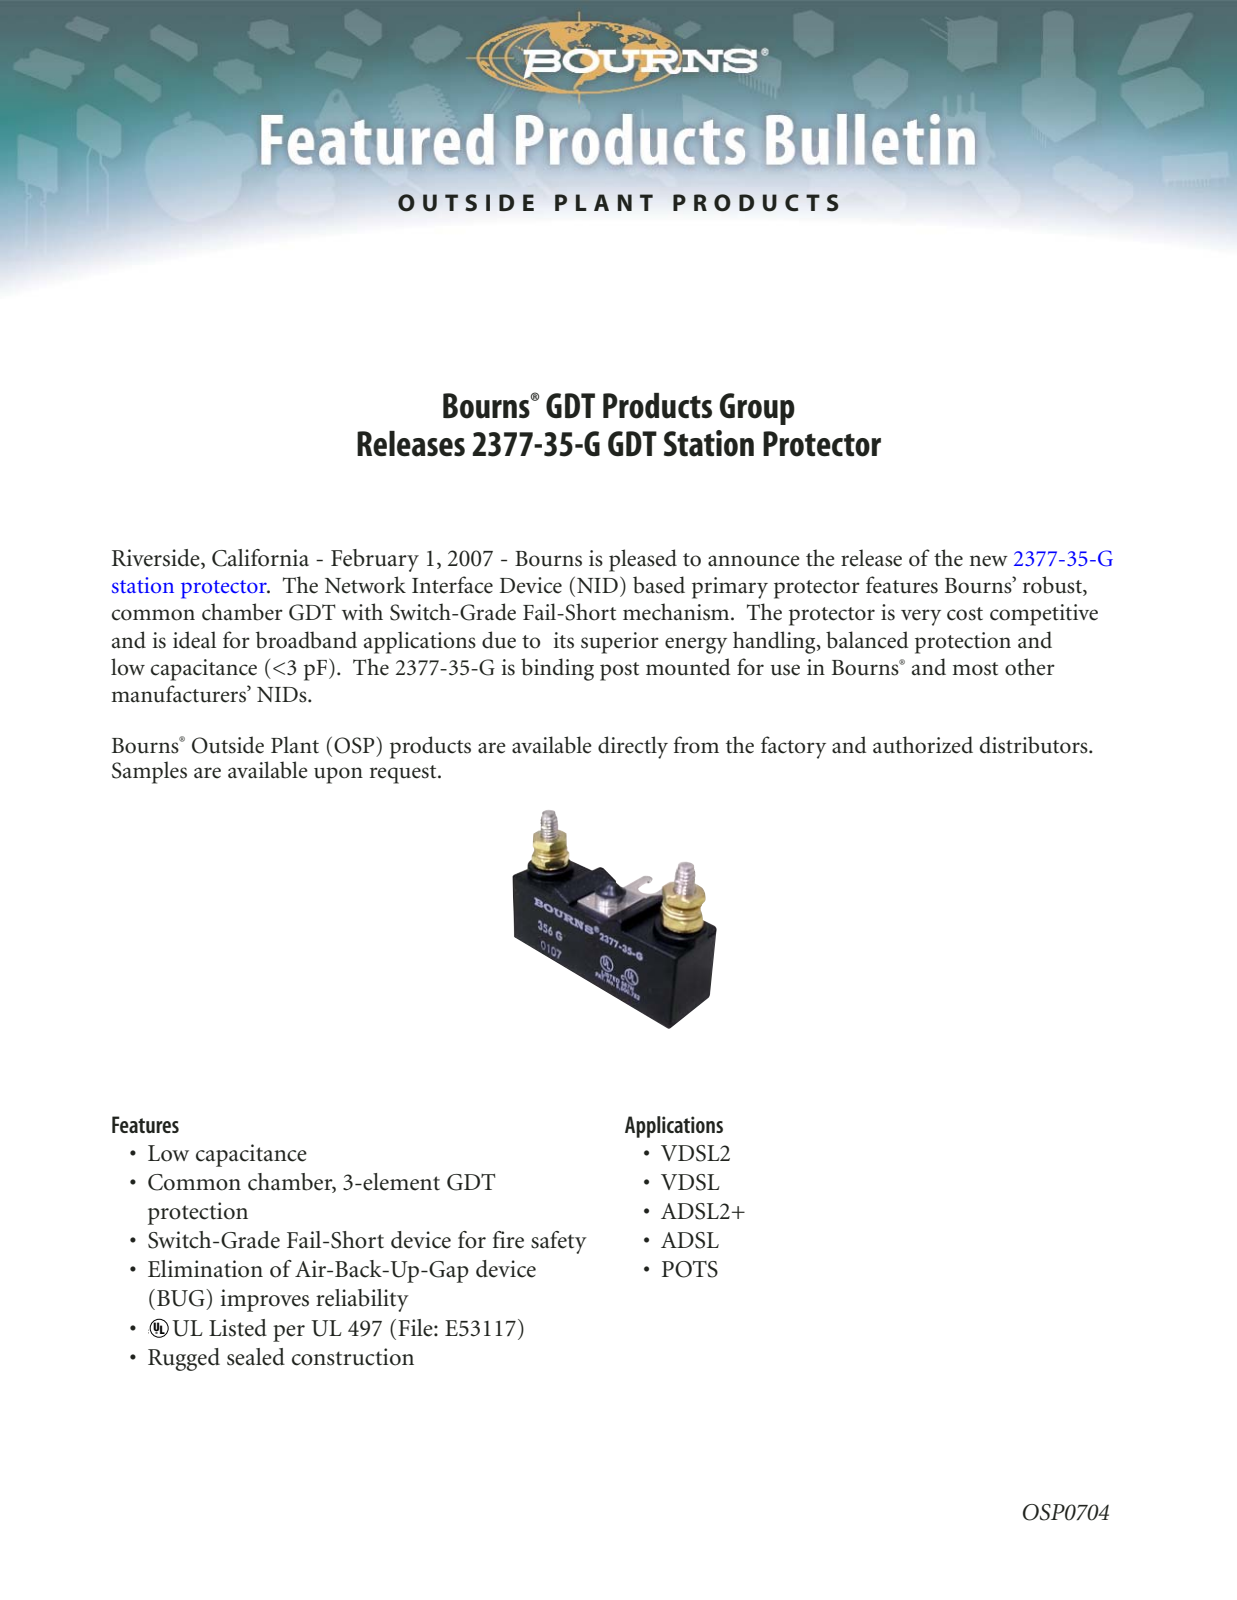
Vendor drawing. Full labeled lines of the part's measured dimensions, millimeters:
Part name (STEP PRODUCT): 2377-45-HS
STEP written by: PRO/ENGINEER BY PARAMETRIC TECHNOLOGY CORPORATION, 2010100 (CONFIG_CONTROL_DESIGN)
Units: millimetres
Bodies: 1 solid, 38 faces (27 planar, 11 cylindrical, 0 other)
Overall size (bounding box): 57.15 × 37.08 × 30.6
Volume: 23 806 mm³ · Surface area: 6 489 mm²
Round bosses / shafts (diameter × count): ⌀12.45 ×2, ⌀7 ×2, ⌀7.87 ×1
Partial cylindrical surfaces — rounded edges, fillets, slot ends (radius × count): R2.79 ×1
Main face-to-face distances: 19.05, 19.7, 57.14, 2.45, 22.15, 5.05, 5.89, 2.6, 3.44, 0.84
